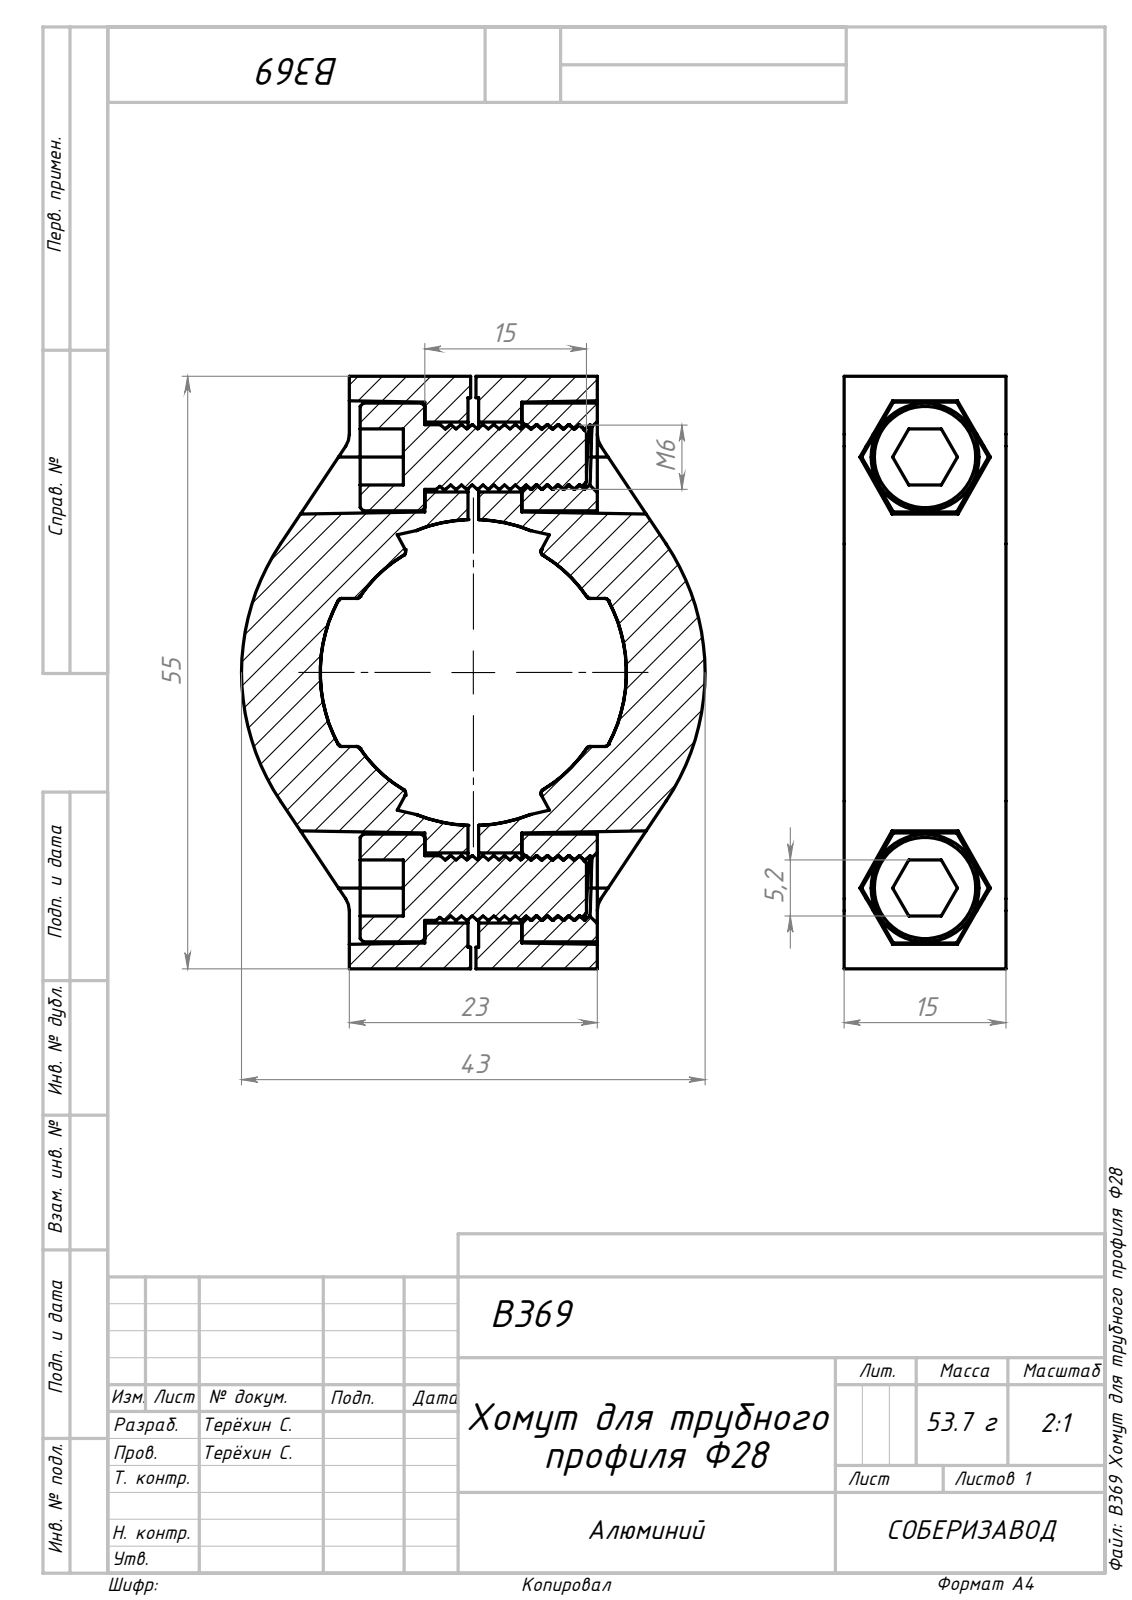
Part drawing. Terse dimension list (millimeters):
name: B369 Хомут для трубного профиля Ф28
written by: SolidWorks 2022 (AUTOMOTIVE_DESIGN)
unit: mm
bodies: 6 solids, 306 faces (104 planar, 116 cylindrical, 86 other)
size: 55 × 43 × 15
volume: 16 616 mm³; area: 10 802 mm²
holes: 2× ⌀5.2, 2× ⌀6.5
bosses: 2× ⌀10, 2× ⌀6
rounds: 12× R0.4, 4× R2, 1× R12.65, 1× R14.2, 1× R21.5
face distances: 15, 20, 10.04, 11, 5, 4, 10, 1, 7, 55
hole spacings: 40
